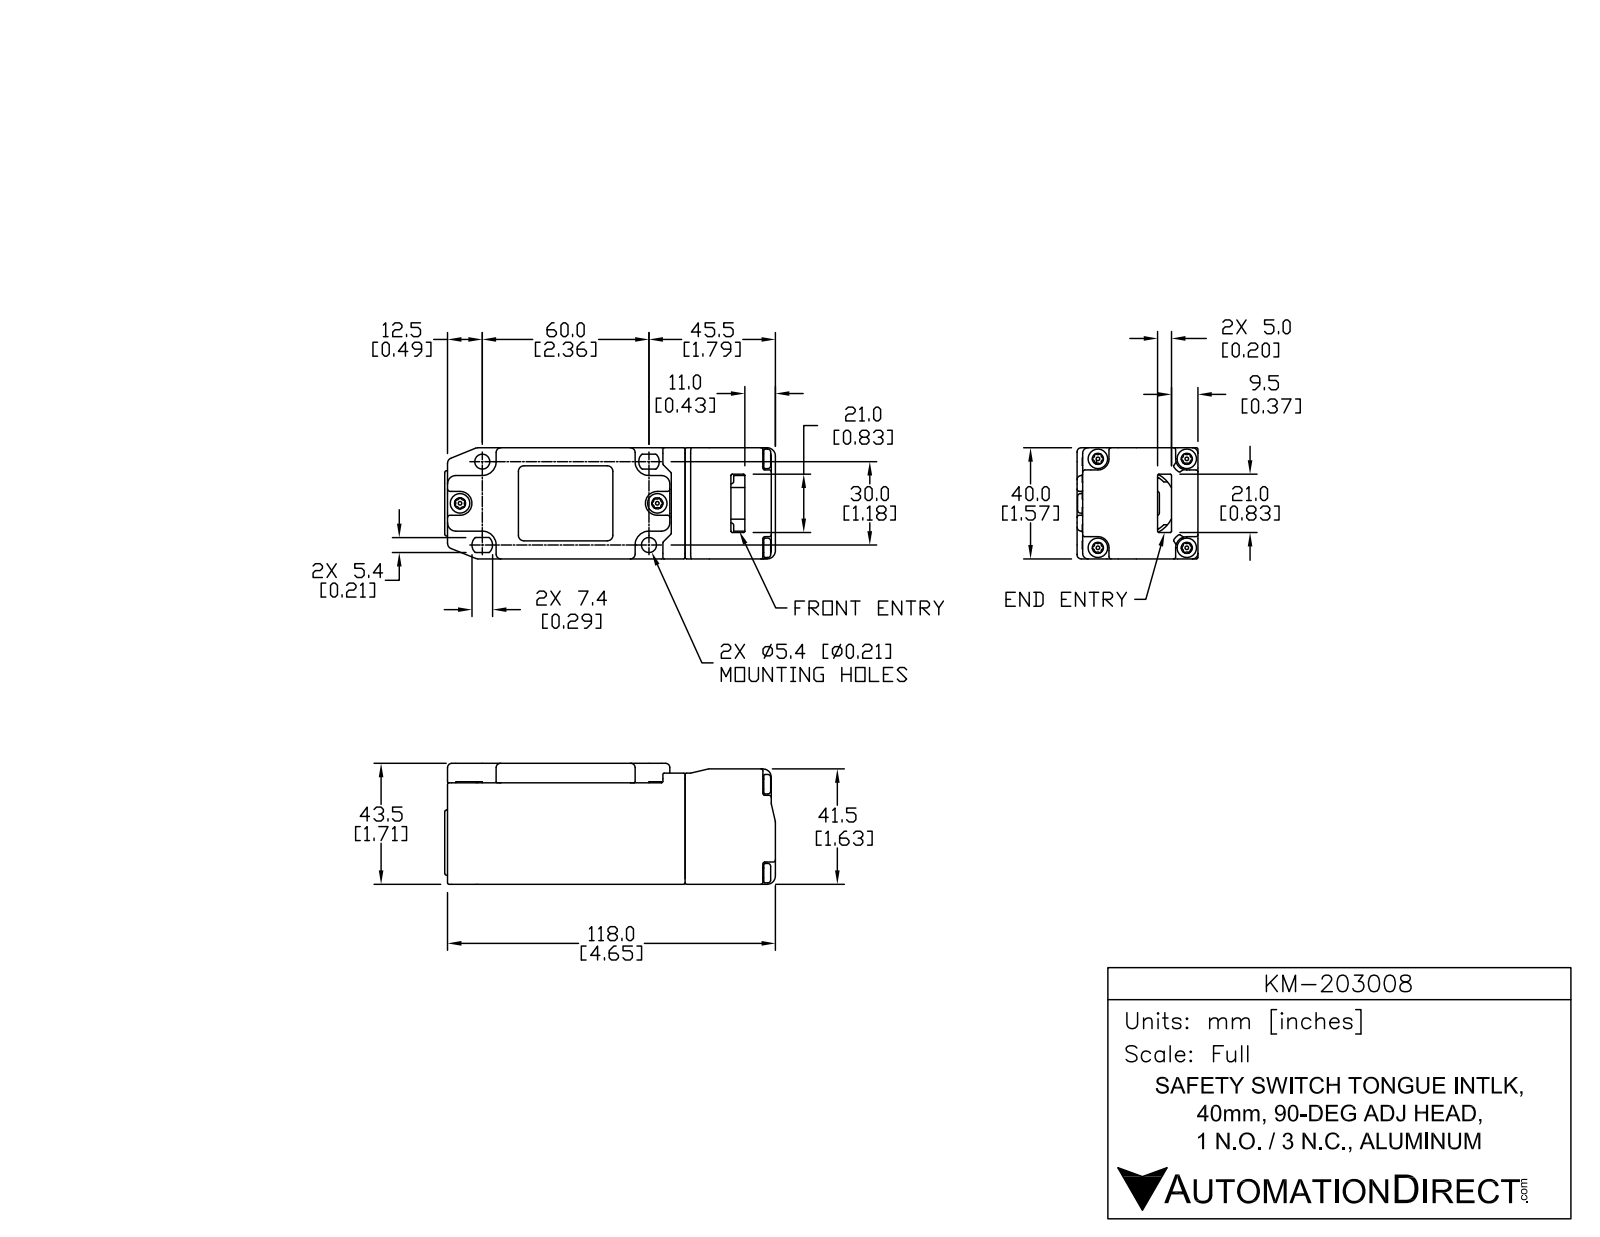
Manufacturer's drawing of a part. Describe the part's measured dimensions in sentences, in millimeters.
The part is named "KM-203008". Its 3-D file was written by "SolidWorks 2013 (AUTOMOTIVE_DESIGN)". It is 1 solid with 581 faces: 128 planar, 263 cylindrical and 190 other. Overall it measures 119.63 by 43.56 by 40 millimeters. Its volume is 183 300 cubic millimeters and its surface area 28 465 square millimeters. Round holes: 2 of diameter 5.4. Round bosses or shafts: 4 of diameter 6.77, 2 of diameter 6.63, 1 of diameter 23, 1 of diameter 5.6. Partial cylindrical surfaces (rounded edges, fillets, slot ends): 95 of radius 0.5, 68 of radius 0.25, 5 of radius 3, 4 of radius 1.45, 4 of radius 1.7, 4 of radius 2.75, 4 of radius 4, 4 of radius 5. The main face-to-face distances are 40, 43.5, 0.5, 43, 118, 2.6, 5, 9.5, 102, 16. The hole center spacings are 67.08.
